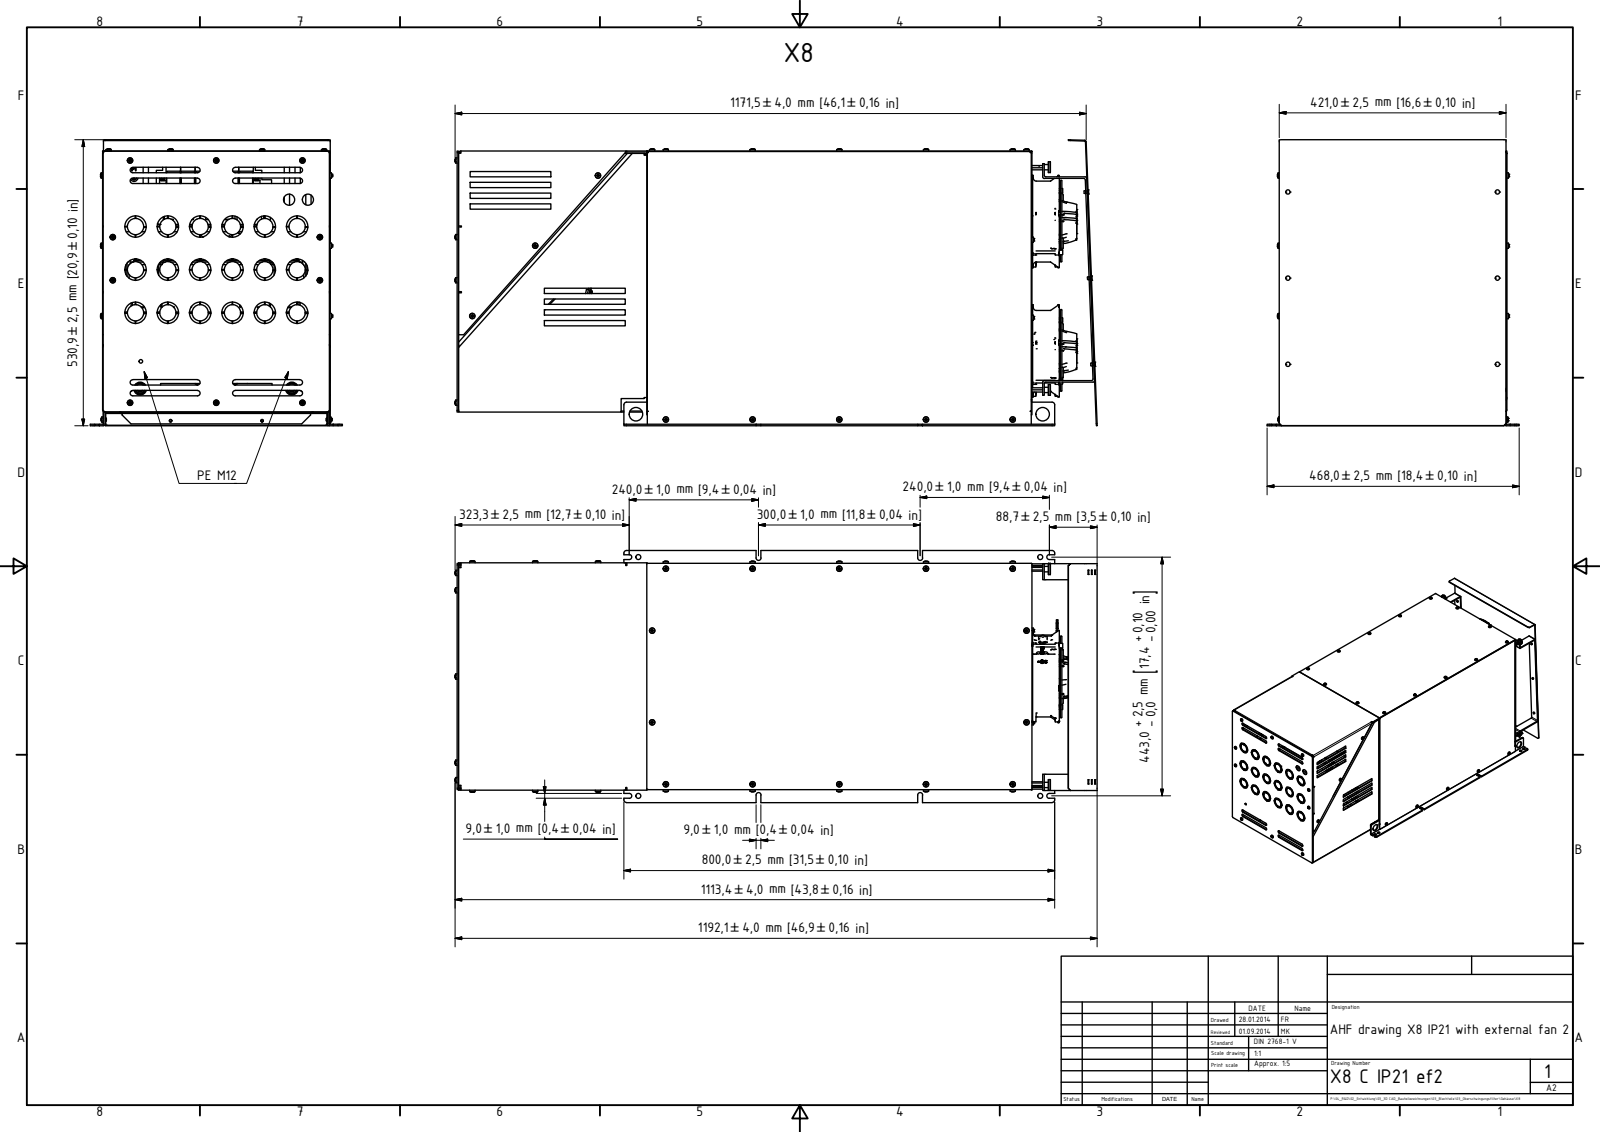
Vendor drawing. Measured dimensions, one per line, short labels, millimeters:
name: 10100531 Seitenwand X8-A1; 10100530 Lüfterblech X8-A1; 10100529 Anschlussblech X8-A1; 10100404 Deckel X7-X8 (+8 more)
written by: Autodesk Inventor 2015 (AUTOMOTIVE_DESIGN)
unit: mm
bodies: 188 solids, 17552 faces (10373 planar, 3170 cylindrical, 4009 other)
size: 1192.06 × 530.87 × 468
volume: 9 388 000 mm³; area: 7 812 000 mm²
holes: 49× ⌀4.13, 47× ⌀6.5, 21× ⌀4, 20× ⌀3.24, 18× ⌀40, 16× ⌀7, 6× ⌀5, 6× ⌀9, 6× ⌀10, 6× ⌀14, 4× ⌀3.95, 4× ⌀4.25
bosses: 51× ⌀5, 45× ⌀4.6, 14× ⌀16, 12× ⌀30, 12× ⌀26.7, 12× ⌀2.5, 10× ⌀8.5, 6× ⌀8
rounds: 412× R0.5, 154× R0.3, 132× R0.83, 115× R1, 65× R3.25, 64× R0.31, 61× R0.1, 57× R2
face distances: 1, 2, 419, 420, 418, 3, 714, 421, 482.5, 1.49
hole spacings: 100, 161, 389, 7.5, 200, 400, 322, 160
